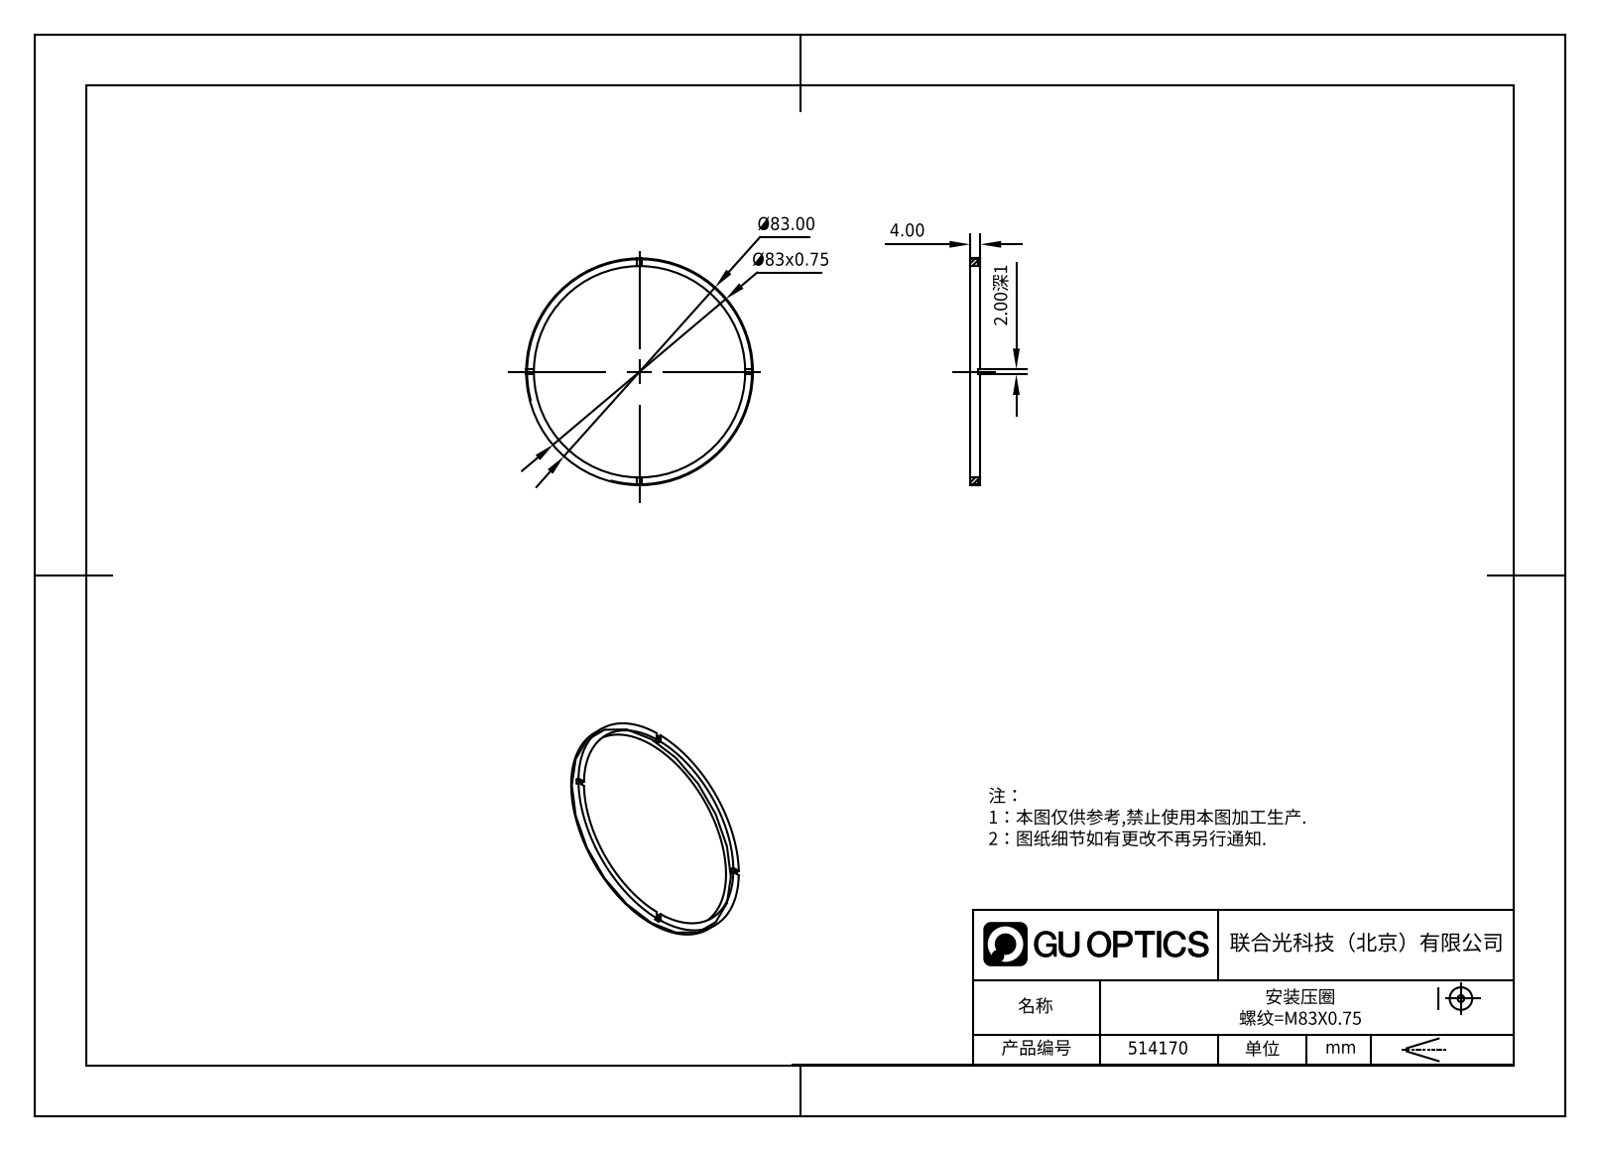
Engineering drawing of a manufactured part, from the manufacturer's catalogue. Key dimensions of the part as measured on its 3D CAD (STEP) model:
Part name (STEP PRODUCT): 514170
STEP written by: SolidWorks 2020 (CONFIG_CONTROL_DESIGN)
Units: millimetres
Bodies: 1 solid, 21 faces (17 planar, 4 cylindrical, 0 other)
Overall size (bounding box): 83 × 83 × 4
Volume: 2 992 mm³ · Surface area: 3 527 mm²
Round holes (diameter × count): ⌀77 ×1
Round bosses / shafts (diameter × count): ⌀83 ×1
Main face-to-face distances: 4, 3, 1, 2
